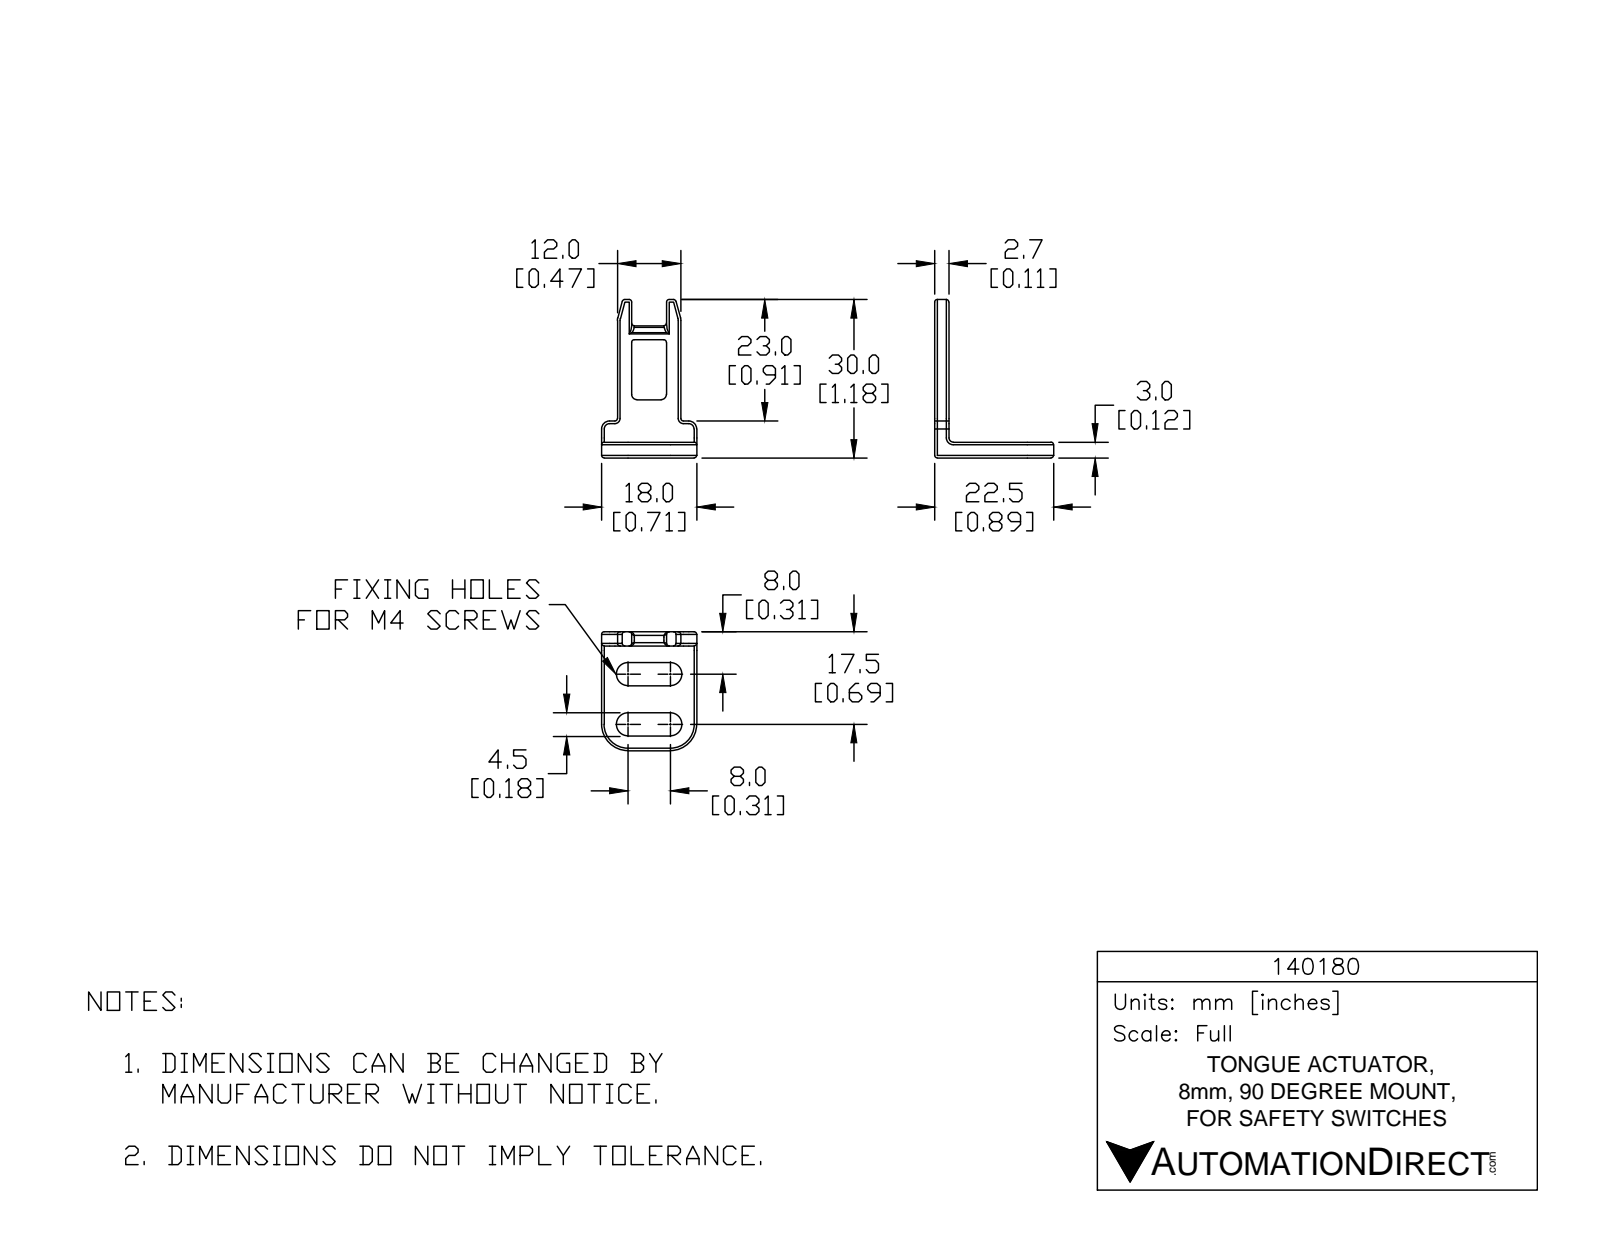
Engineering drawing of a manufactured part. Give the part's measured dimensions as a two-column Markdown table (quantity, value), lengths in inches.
| quantity | value |
| --- | --- |
| part name | 140180 |
| STEP written by | SolidWorks 2014 (AUTOMOTIVE_DESIGN) |
| units | inches |
| bodies | 1 solid, 168 faces (28 planar, 76 cylindrical, 64 other) |
| overall size | 1.181 × 0.886 × 0.709 |
| volume | 0.091 in³ |
| surface area | 2.493 in² |
| partial cylindrical surfaces (radius × count) | 0.02 × 53, 0.087 × 4, 0.039 × 2, 0.059 × 2, 0.079 × 2, 0.197 × 2, 0.031 × 1 |
| main face-to-face distances | 0.118, 0.106, 0.484, 0.591, 0.224, 0.366, 0.709, 0.173, 0.374, 0.472 |
